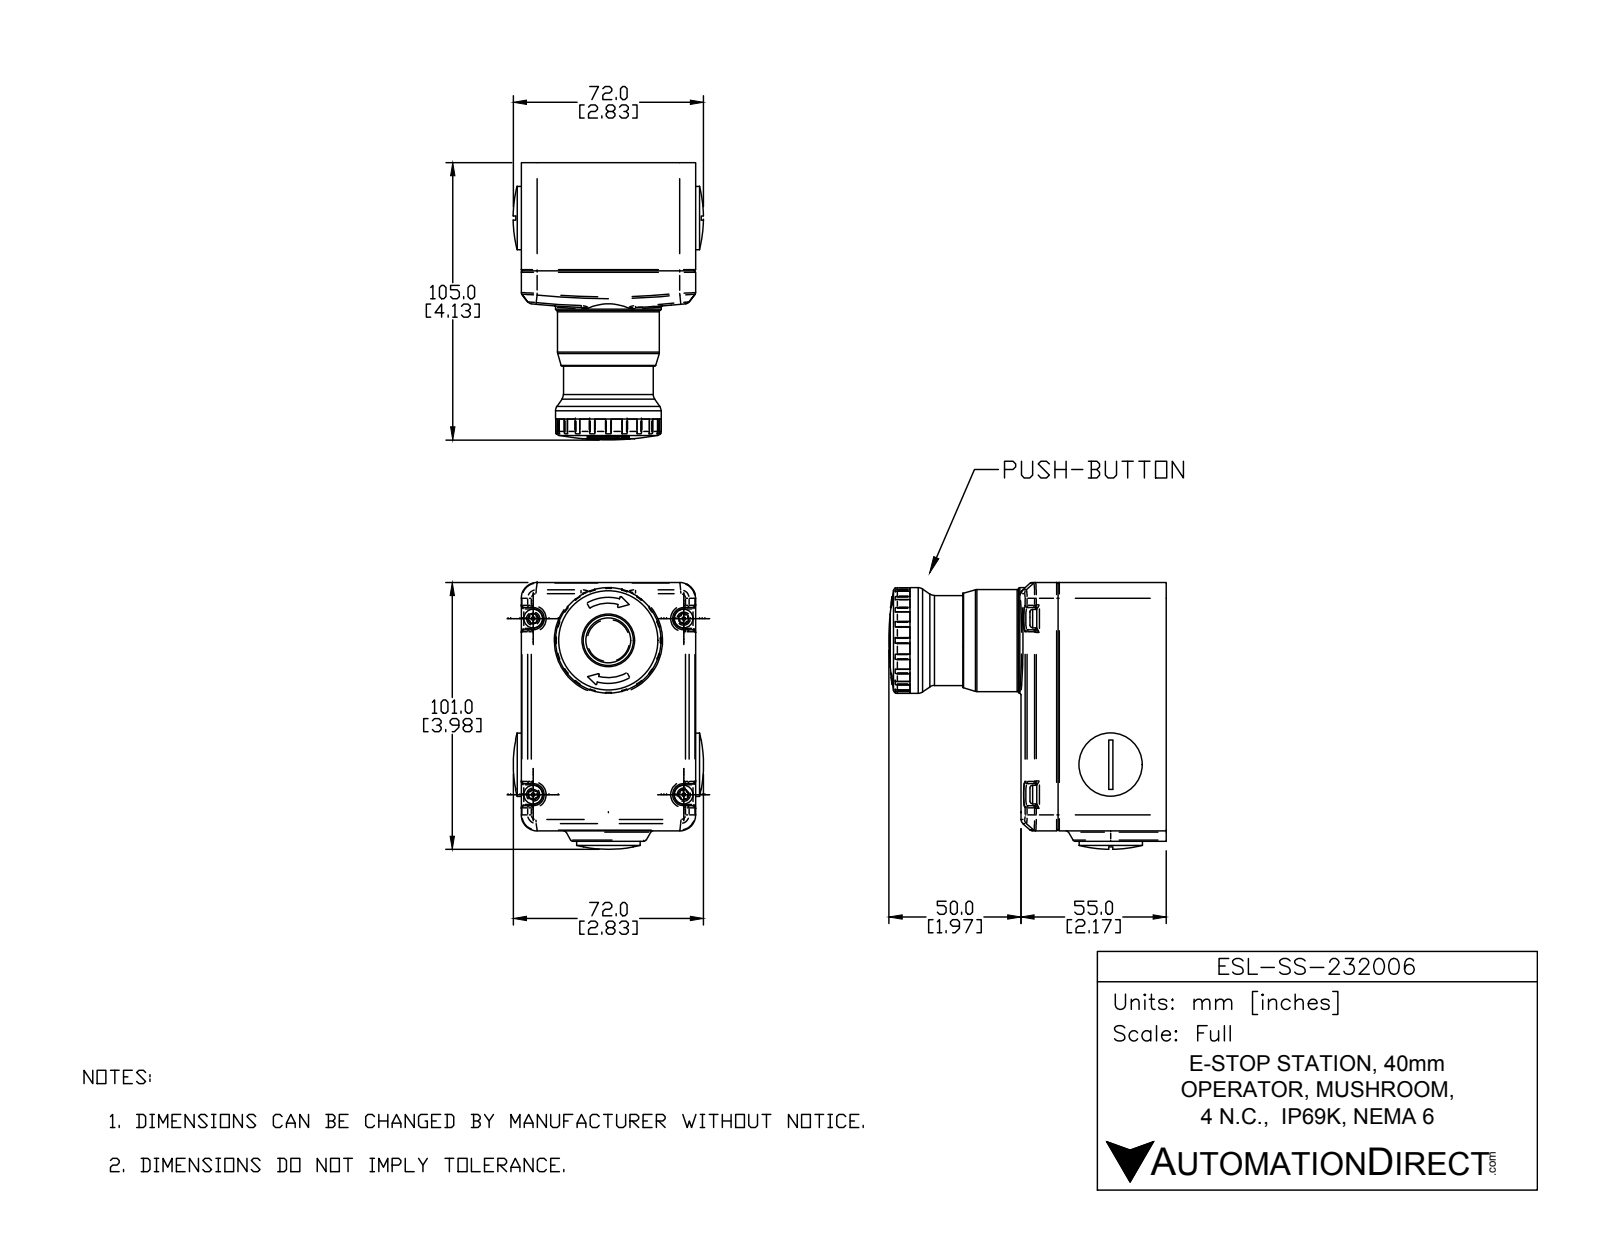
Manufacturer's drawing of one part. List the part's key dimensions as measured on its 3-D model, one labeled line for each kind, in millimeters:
Part name (STEP PRODUCT): ESL-SS-232006
STEP written by: SolidWorks 2016 (AUTOMOTIVE_DESIGN)
Units: millimetres
Bodies: 11 solids, 674 faces (216 planar, 248 cylindrical, 210 other)
Overall size (bounding box): 105 × 100.99 × 71.98
Volume: 363 454 mm³ · Surface area: 60 089 mm²
Round holes (diameter × count): ⌀4.5 ×4, ⌀31.1 ×1, ⌀37 ×1
Round bosses / shafts (diameter × count): ⌀7 ×4, ⌀1 ×4, ⌀24 ×2, ⌀40 ×1, ⌀38.6 ×1, ⌀34 ×1
Partial cylindrical surfaces — rounded edges, fillets, slot ends (radius × count): R0.1 ×80, R0.76 ×24, R0.5 ×14, R0.2 ×4, R1 ×4, R4.2 ×4, R6 ×4, R2 ×2
Main face-to-face distances: 41, 66, 56, 15, 98, 4, 94, 56.8, 15.8, 0.8
Hole centre spacings: 31.38, 54, 71.31, 82, 98.18
